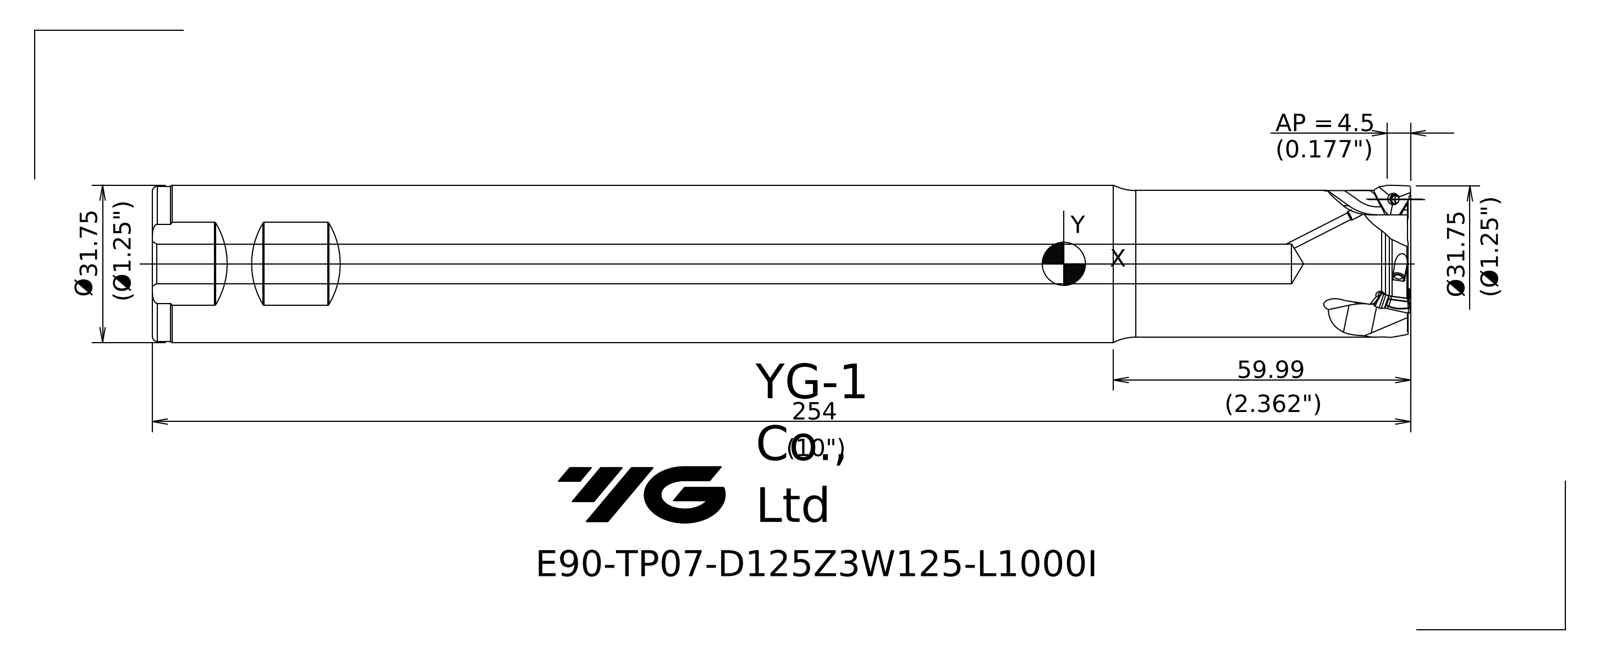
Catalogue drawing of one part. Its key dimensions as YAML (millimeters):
part_name: "102221B476C3yzxm"
step_written_by: "SIEMENS PLM Software NX 10.0 (AP203_CONFIGURATION_CONTROLLED_3D_DESIGN_OF_MECHANICAL_PARTS_AND_ASSEMBLIES_MIM_LF)"
units: millimeters
bodies: {solids: 1, faces: 51, planar: 8, cylindrical: 8, other: 35}
overall_size: [254, 31.81, 31.81]
volume: 182241
surface_area: 34015
round_holes:
  - {diameter: 1.5, count: 1}
  - {diameter: 8, count: 1}
round_bosses_or_shafts:
  - {diameter: 31.75, count: 1}
  - {diameter: 31.35, count: 1}
  - {diameter: 29.6, count: 1}
partial_cylinders:
  - {radius: 0.3, count: 3}
face_to_face_distances: [253.35, 253.5, 16.13]
